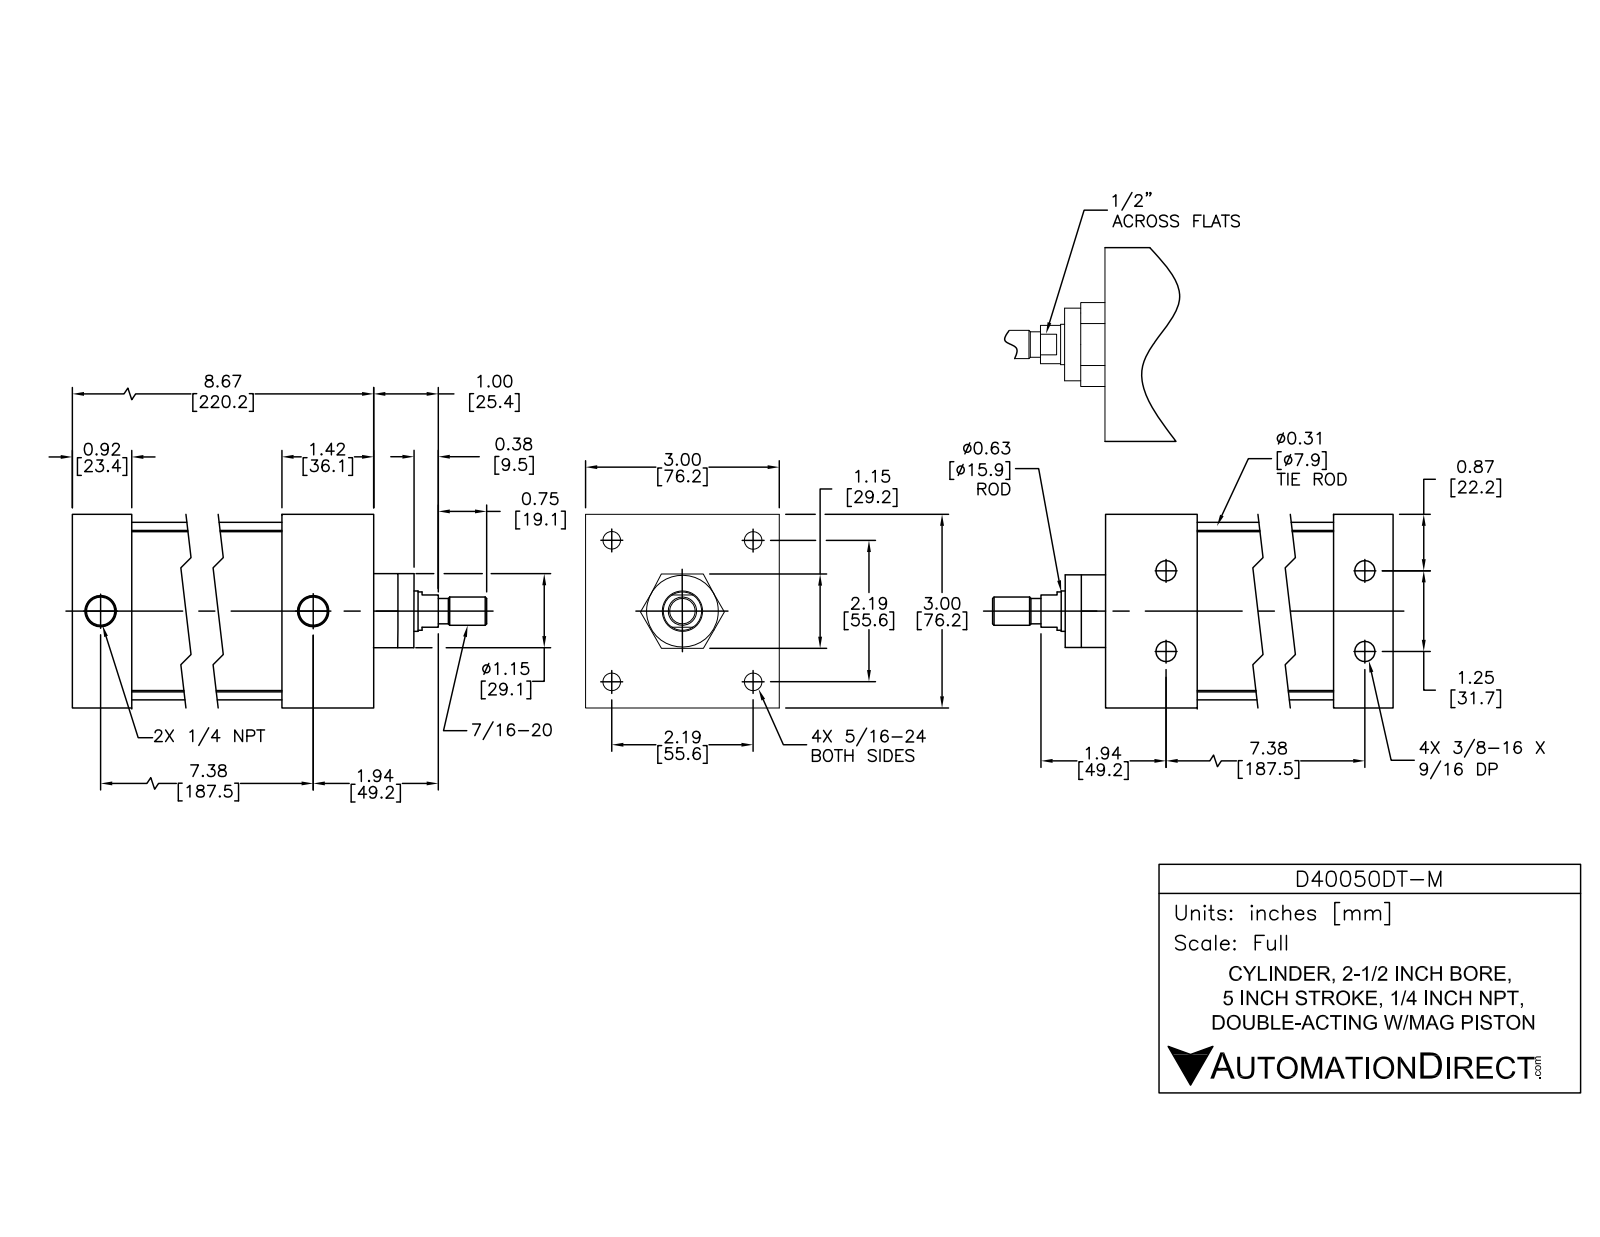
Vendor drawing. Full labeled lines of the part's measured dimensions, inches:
Part name (STEP PRODUCT): D40050DT-M; D40050DT-M PISTON; D40050DT-M BODY
STEP written by: SolidWorks 2015 (AUTOMOTIVE_DESIGN)
Units: inches
Bodies: 12 solids, 298 faces (94 planar, 114 cylindrical, 90 other)
Overall size (bounding box): 10.496 × 3 × 3
Volume: 37.14 in³ · Surface area: 262.6 in²
Round holes (diameter × count): ⌀0.267 ×4, ⌀0.307 ×4, ⌀0.359 ×4, ⌀0.5 ×4, ⌀0.297 ×2, ⌀0.477 ×2, ⌀0.625 ×1, ⌀0.628 ×1, ⌀2.5 ×1
Round bosses / shafts (diameter × count): ⌀0.484 ×4, ⌀0.313 ×4, ⌀0.282 ×4, ⌀2.75 ×1, ⌀2.497 ×1, ⌀1.12 ×1, ⌀0.622 ×1, ⌀0.59 ×1
Partial cylindrical surfaces — rounded edges, fillets, slot ends (radius × count): R0.3 ×4
Main face-to-face distances: 3, 0.08, 6.326, 8.746, 7.726, 1.02, 1.42, 6.306, 7.326, 1
Hole centre spacings: 1.556, 2.2, 7.396, 7.37, 0.625, 0.625, 1.25, 3.111
